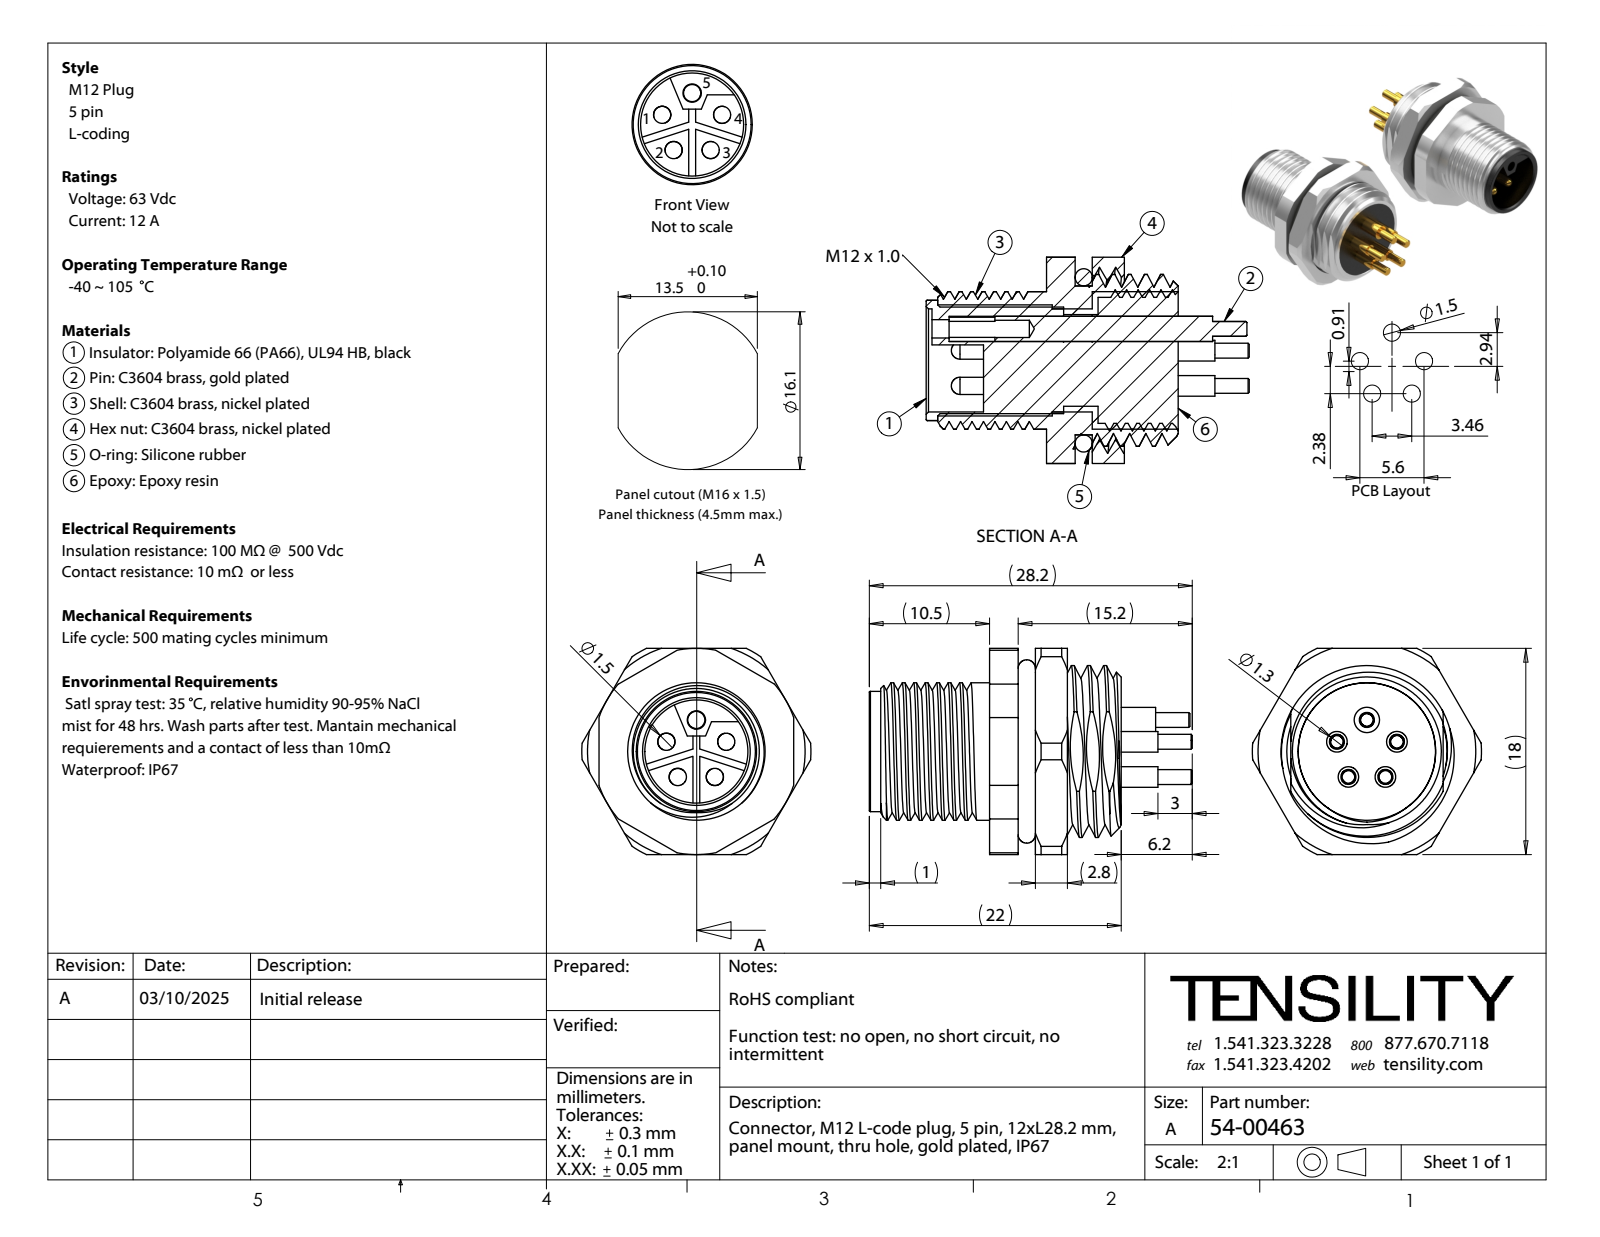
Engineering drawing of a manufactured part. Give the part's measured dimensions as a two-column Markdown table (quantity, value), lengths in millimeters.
| quantity | value |
| --- | --- |
| part name | 54-00463-04; 54-00463-02; 54-00463; 54-00463-01 (+3 more) |
| STEP written by | SolidWorks 2021 (CONFIG_CONTROL_DESIGN) |
| units | millimeters |
| bodies | 9 solids, 358 faces (101 planar, 153 cylindrical, 104 other) |
| overall size | 28.2 × 20 × 18 |
| volume | 3 209 mm³ |
| surface area | 5 915 mm² |
| round holes (diameter × count) | 1.5 × 5, 1.6 × 1, 8 × 1, 9 × 1, 9.3 × 1, 11 × 1, 14 × 1 |
| round bosses / shafts (diameter × count) | 1.3 × 5, 1.8 × 4, 13 × 1, 12 × 1, 10.5 × 1, 9.7 × 1, 2.2 × 1 |
| partial cylindrical surfaces (radius × count) | 7.5 × 1, 9 × 1, 10 × 1 |
| main face-to-face distances | 4, 1.5, 11.5, 9, 7.5, 2.5, 4.7, 2.8, 4.3, 6.8 |
| hole center spacings | 2.75, 5.23, 3.24, 3.23, 5.24 |
